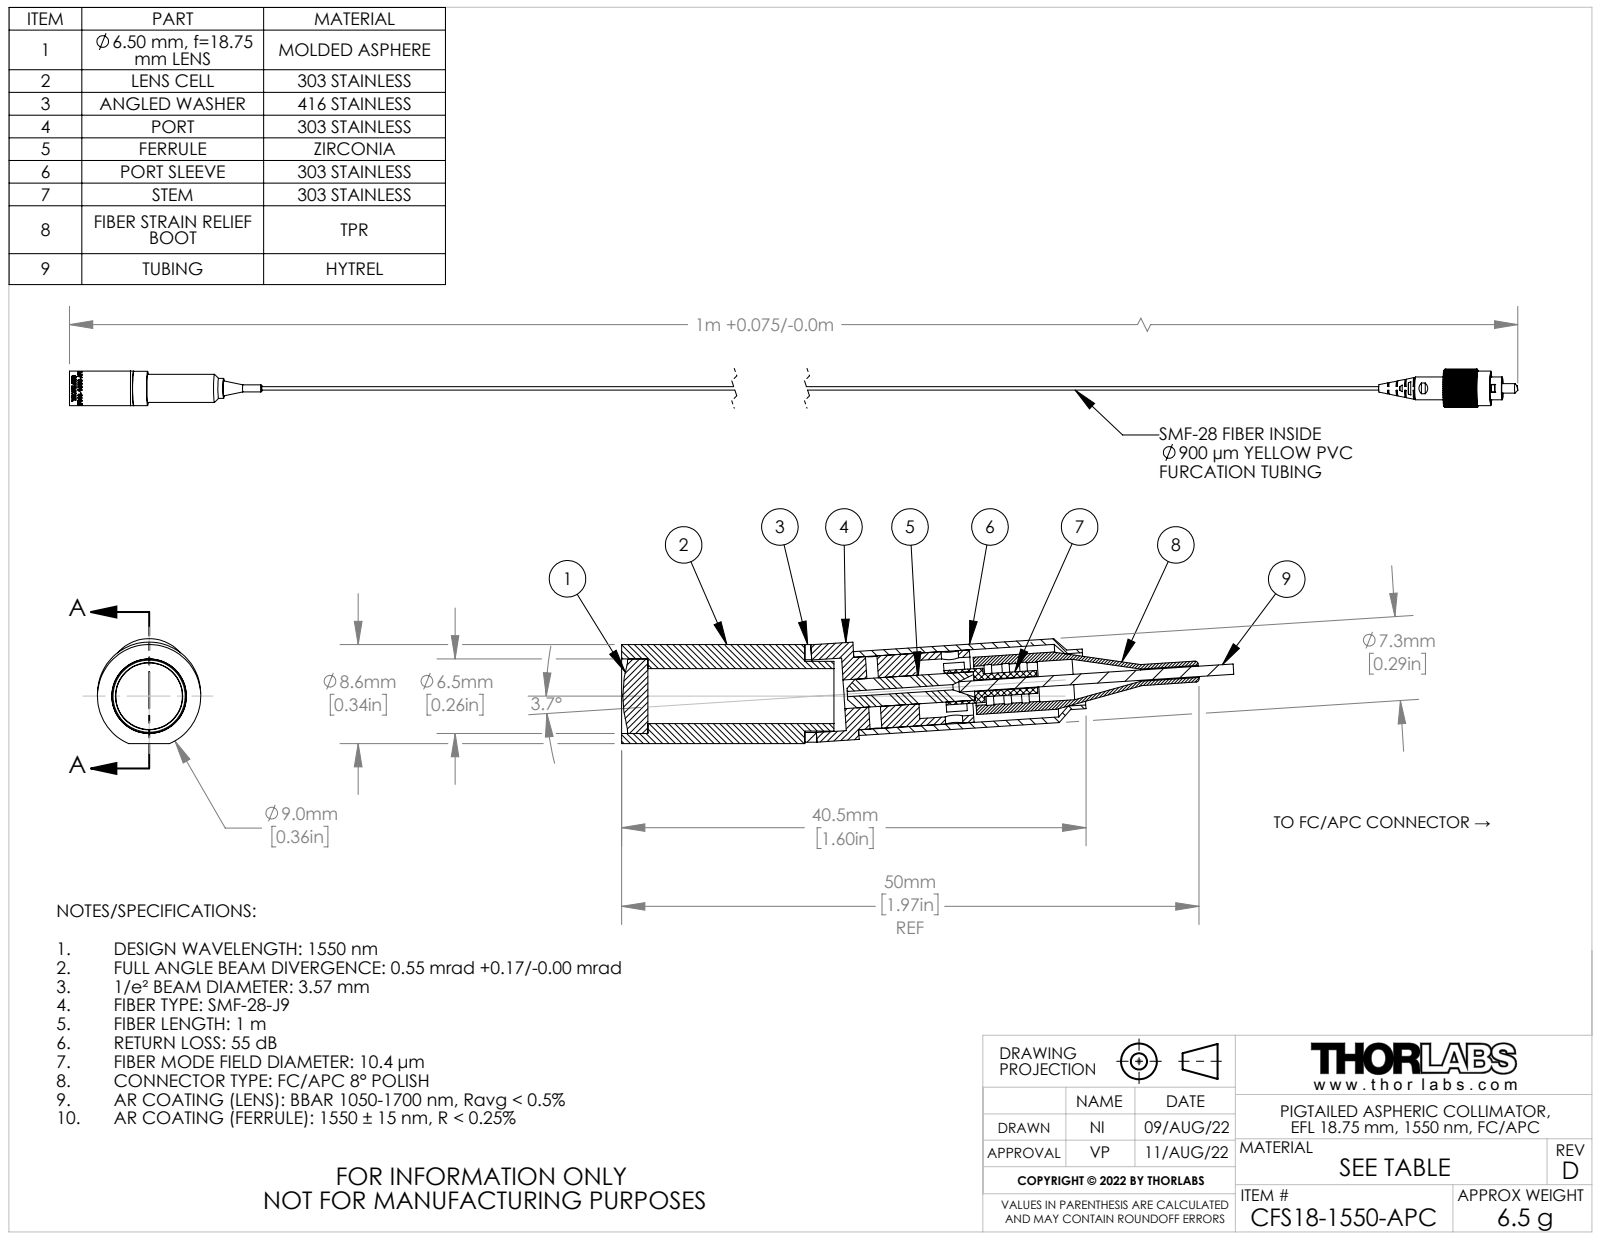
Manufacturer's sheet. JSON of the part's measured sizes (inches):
{"part_name": "17372-E0W", "step_written_by": "SolidWorks 2018 (CONFIG_CONTROL_DESIGN)", "units": "inches", "bodies": {"solids": 12, "faces": 530, "planar": 254, "cylindrical": 224, "other": 52}, "overall_size": [40.895, 2.933, 0.393], "volume_in3": 0.179, "surface_area_in2": 12.74, "round_holes": [[0.04, 2], [0.059, 2], [0.2, 2], [0.25, 2], [0.018, 1], [0.039, 1], [0.042, 1], [0.055, 1], [0.098, 1], [0.098, 1], [0.119, 1], [0.12, 1]], "round_bosses_or_shafts": [[0.235, 2], [0.098, 2], [0.355, 1], [0.354, 1], [0.289, 1], [0.28, 1], [0.256, 1], [0.249, 1]], "partial_cylinders_radius": [[0.089, 1], [0.117, 1], [0.197, 1]], "face_to_face_distances": [0.267, 39.719, 0.267, 0.145, 39.574, 0.04, 0.103, 39.759, 39.614, 0.63], "hole_center_spacings": [0.02, 0.02, 0.27]}
